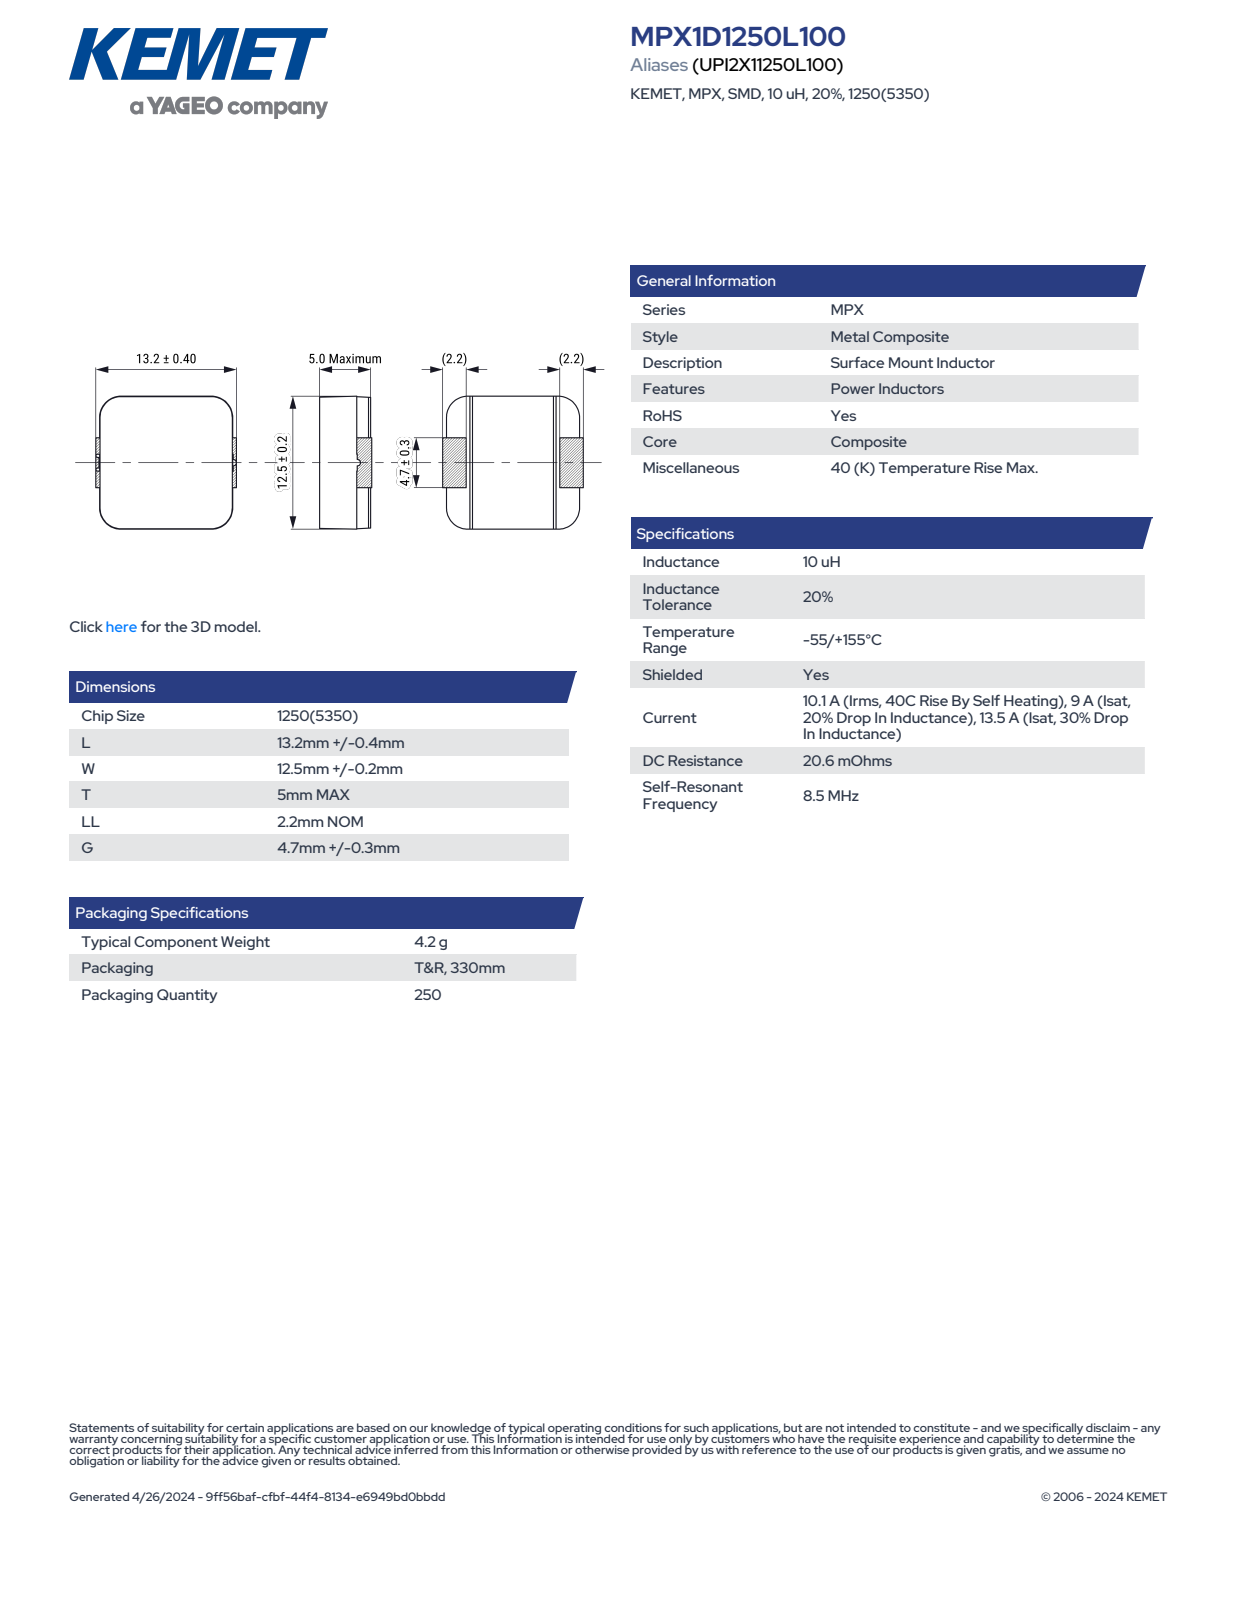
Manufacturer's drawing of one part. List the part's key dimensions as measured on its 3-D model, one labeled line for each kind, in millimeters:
Part name (STEP PRODUCT): MPX1D1250(4_7)(KEMET)
STEP written by: SolidWorks 2018 (AUTOMOTIVE_DESIGN)
Units: millimetres
Bodies: 1 solid, 122 faces (105 planar, 17 cylindrical, 0 other)
Overall size (bounding box): 13.6 × 12.7 × 5.06
Volume: 773 mm³ · Surface area: 576 mm²
Partial cylindrical surfaces — rounded edges, fillets, slot ends (radius × count): R0.26 ×4, R1.96 ×4, R2 ×4, R0.15 ×3
Main face-to-face distances: 5, 4.8, 5.06, 13.34, 1.1, 13.08, 13.6, 1.3, 1.36, 3.7
